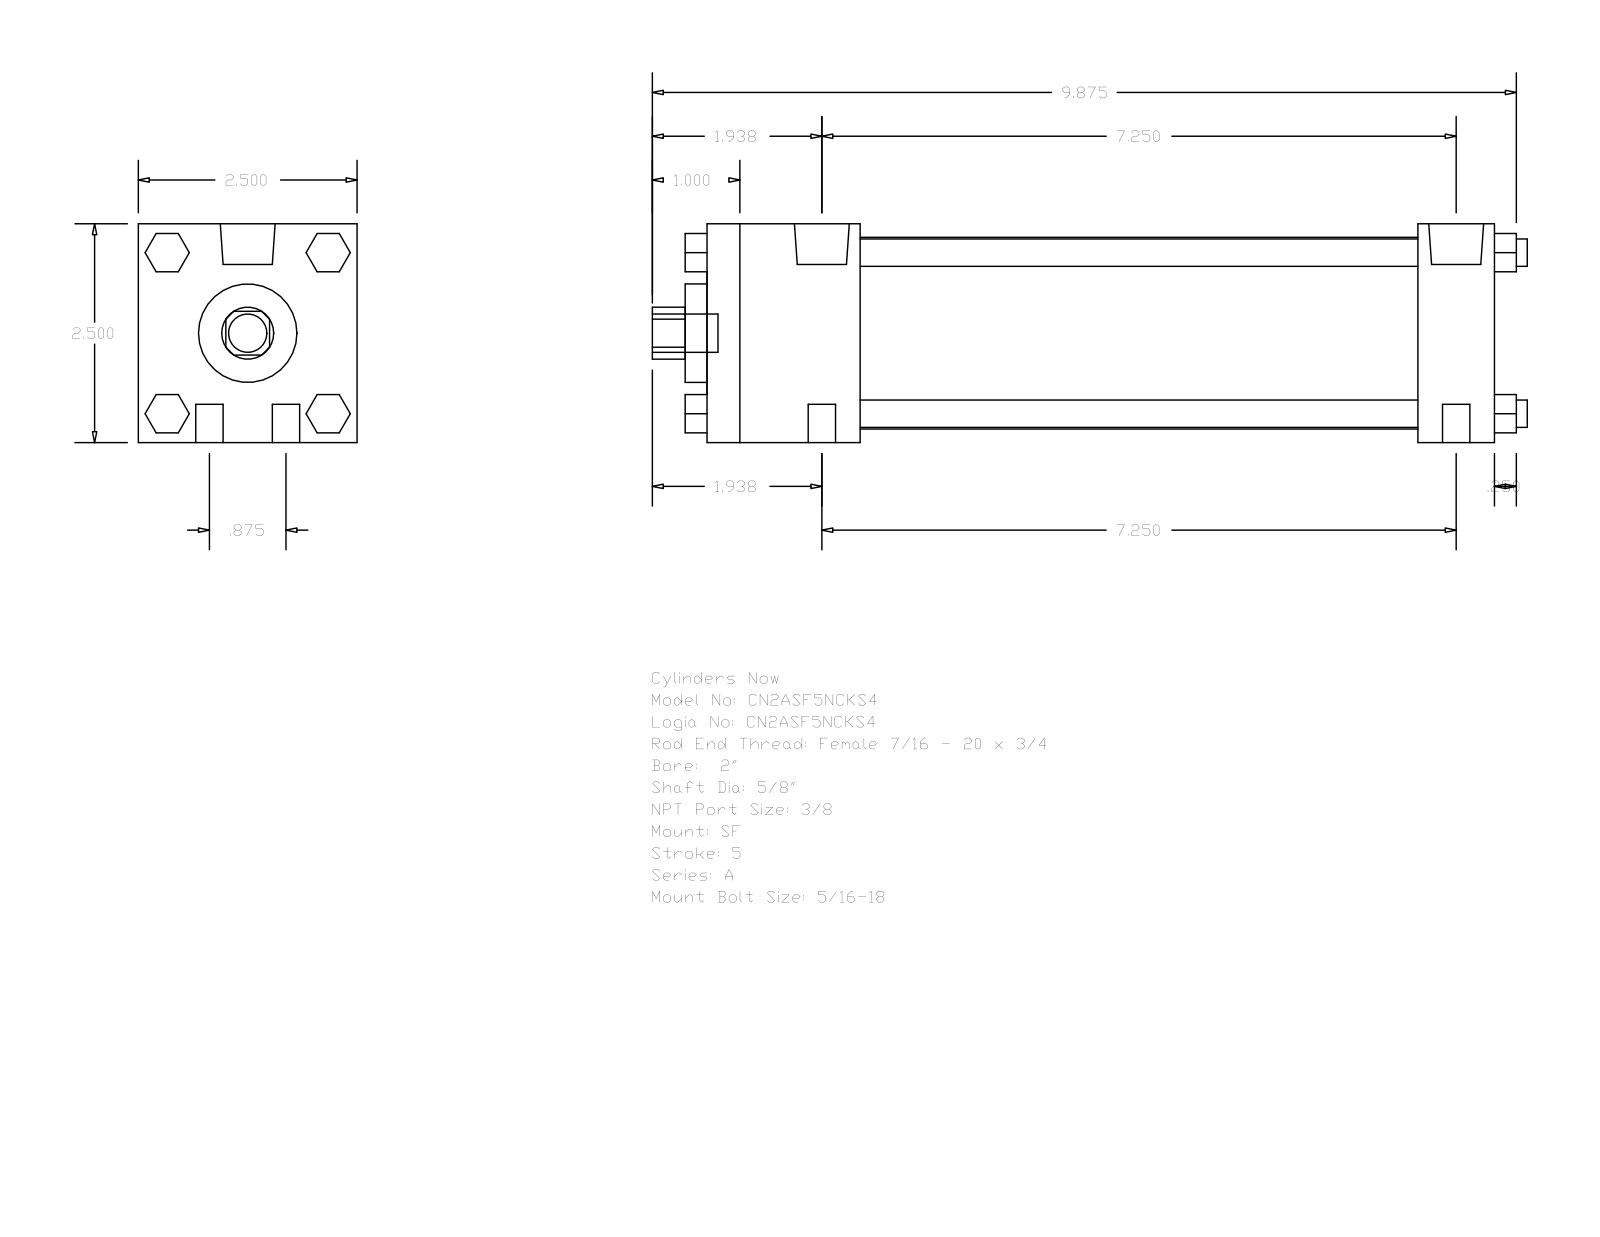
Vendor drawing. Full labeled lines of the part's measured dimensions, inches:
Part name (STEP PRODUCT): A_SF__0200_0.625
STEP written by: GSSL Pune (CONFIG_CONTROL_DESIGN)
Units: inches
Bodies: 0 solids, 124 faces (94 planar, 30 cylindrical, 0 other)
Overall size (bounding box): 10 × 2.5 × 2.5
Round holes (diameter × count): ⌀0.625 ×1, ⌀1.125 ×1, ⌀2.19 ×1
Round bosses / shafts (diameter × count): ⌀0.313 ×8, ⌀0.627 ×2, ⌀0.219 ×2, ⌀0.437 ×1
Partial cylindrical surfaces — rounded edges, fillets, slot ends (radius × count): R0.297 ×1
Main face-to-face distances: 2.5, 9, 8.125, 0.875, 1.75, 6.375, 7.25, 0.25, 9.25, 2
